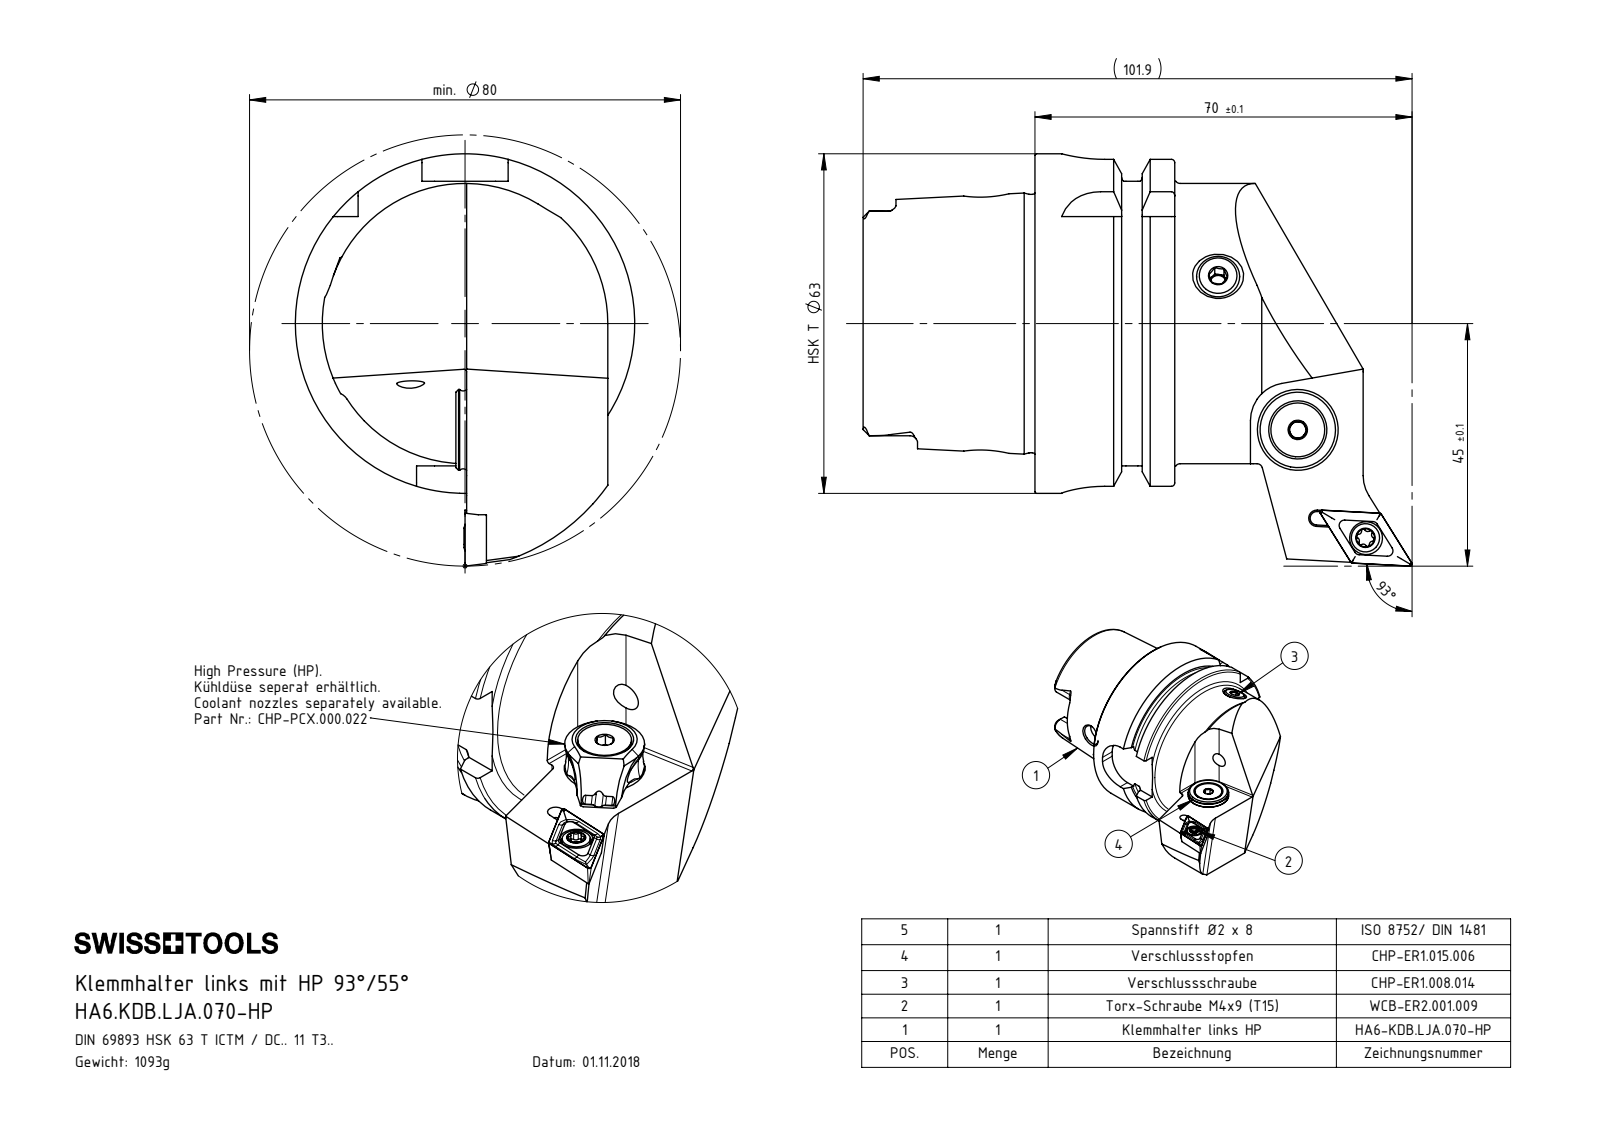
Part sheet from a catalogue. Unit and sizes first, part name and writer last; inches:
Units: inches
Overall size (bounding box): 4.012 × 3.012 × 2.48
Round holes (diameter × count): ⌀0.165 ×2, ⌀0.197 ×2, ⌀0.047 ×1, ⌀0.079 ×1, ⌀0.098 ×1, ⌀0.118 ×1, ⌀0.13 ×1, ⌀0.173 ×1, ⌀0.205 ×1, ⌀0.24 ×1, ⌀0.276 ×1, ⌀0.295 ×1
Round bosses / shafts (diameter × count): ⌀2.48 ×1, ⌀2.163 ×1, ⌀2.047 ×1, ⌀1.887 ×1, ⌀0.591 ×1, ⌀0.528 ×1, ⌀0.394 ×1, ⌀0.315 ×1
Partial cylindrical surfaces — rounded edges, fillets, slot ends (radius × count): R0.013 ×6, R0.023 ×6, R0.055 ×6, R0.315 ×4, R0.02 ×2, R0.111 ×2, R0.113 ×2, R0.276 ×2
Main face-to-face distances: 1.022, 0.63, 0.392, 1.031, 1.256, 1.648, 2.278, 2.079, 0.858, 0.467
Hole centre spacings: 0.177, 0.82, 0.824, 0.93, 0.935, 1.819, 1.992, 2.651
Volume: 8.471 in³ · Surface area: 50.35 in²
Bodies: 8 solids, 418 faces (119 planar, 121 cylindrical, 178 other)
Part name (STEP PRODUCT): DIN 3771 - 13x1; CHP-ER1.015.006; CHP-ER1.008.014_A; ISO 8752 2x8 (+6 more)
STEP written by: SolidWorks 2017 (AUTOMOTIVE_DESIGN)
